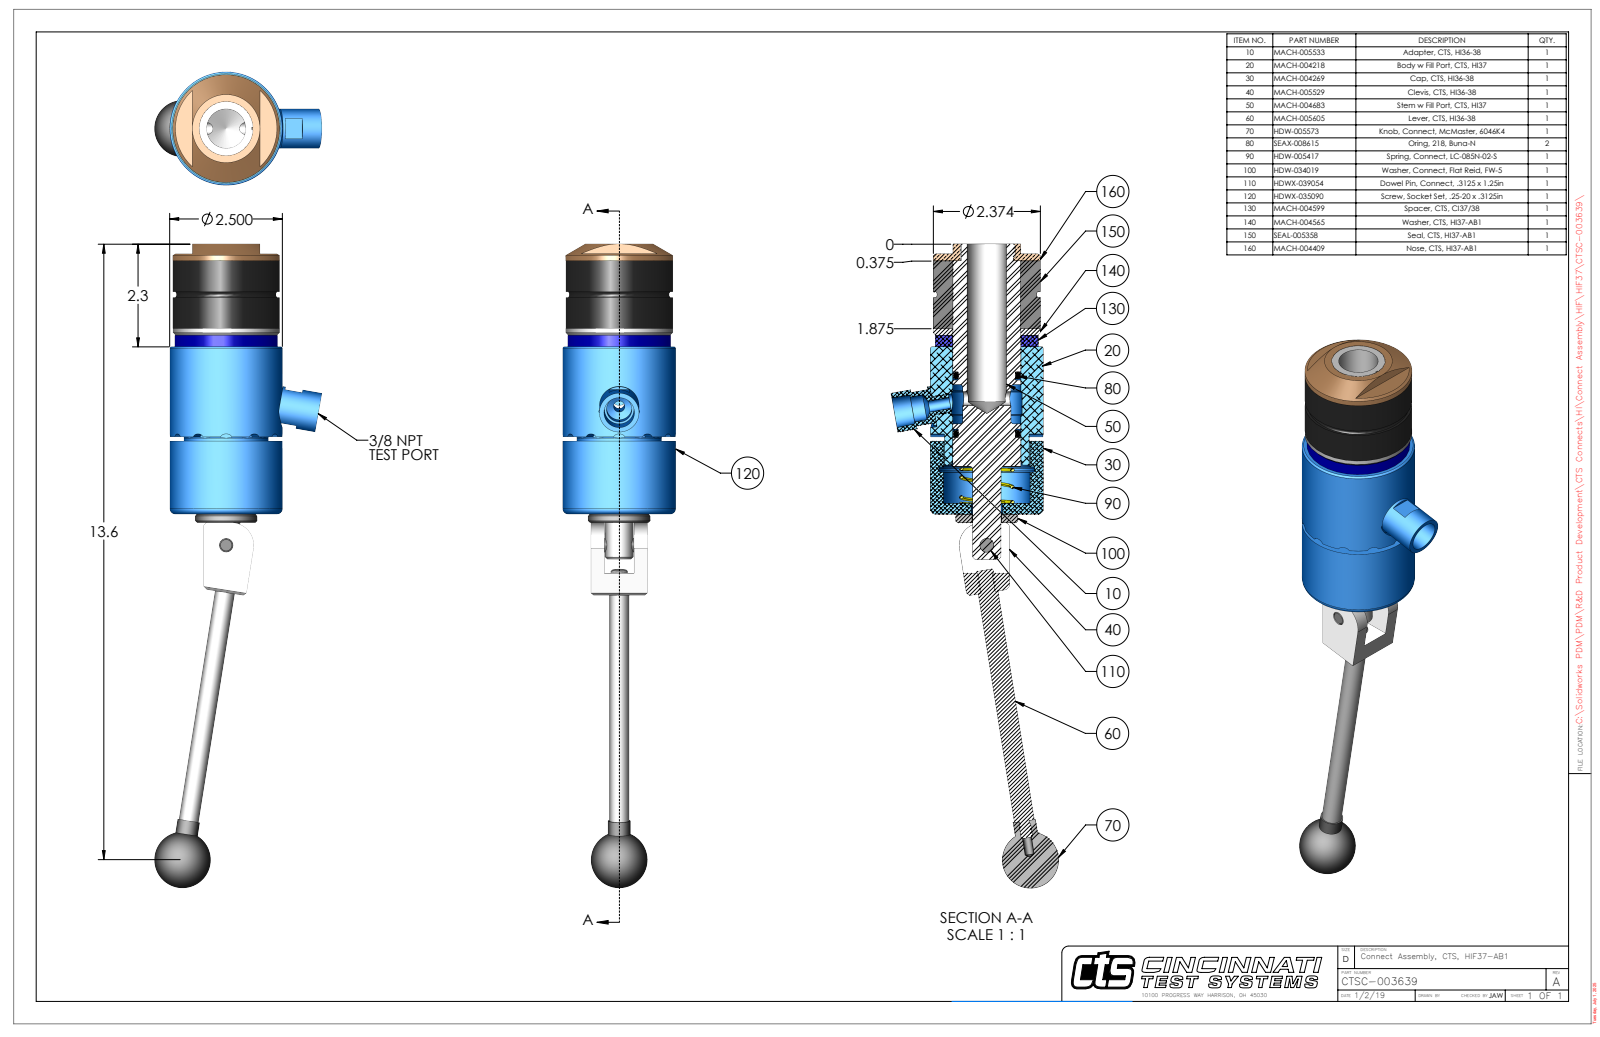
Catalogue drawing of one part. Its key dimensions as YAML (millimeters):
part_name: "CTSC-003639"
step_written_by: "SolidWorks 2023 (AUTOMOTIVE_DESIGN)"
units: millimeters
bodies: {solids: 10, faces: 307, planar: 108, cylindrical: 126, other: 73}
overall_size: [362.6, 94.4, 63.5]
volume: 477400
surface_area: 96520
round_holes:
  - {diameter: 5.1, count: 2}
  - {diameter: 3.8, count: 1}
  - {diameter: 6.4, count: 1}
  - {diameter: 7.9, count: 1}
  - {diameter: 7.9, count: 1}
  - {diameter: 8, count: 1}
  - {diameter: 8, count: 1}
  - {diameter: 14.3, count: 1}
  - {diameter: 16.7, count: 1}
  - {diameter: 17.7, count: 1}
  - {diameter: 22.2, count: 1}
  - {diameter: 29.8, count: 1}
round_bosses_or_shafts:
  - {diameter: 63.5, count: 1}
  - {diameter: 60.3, count: 1}
  - {diameter: 57.9, count: 1}
  - {diameter: 47.6, count: 1}
  - {diameter: 38.1, count: 1}
  - {diameter: 38, count: 1}
  - {diameter: 35.1, count: 1}
  - {diameter: 31.8, count: 1}
partial_cylinders:
  - {radius: 3, count: 12}
  - {radius: 0.7, count: 2}
  - {radius: 4.8, count: 1}
  - {radius: 5, count: 1}
  - {radius: 11.9, count: 1}
  - {radius: 12, count: 1}
  - {radius: 12.7, count: 1}
  - {radius: 30.7, count: 1}
face_to_face_distances: [38.1, 10.2, 48.3, 6.4, 94.3, 104.5, 142.6, 100.7, 3.9, 42]
hole_center_spacings: [18.8, 53.8, 72.6]
